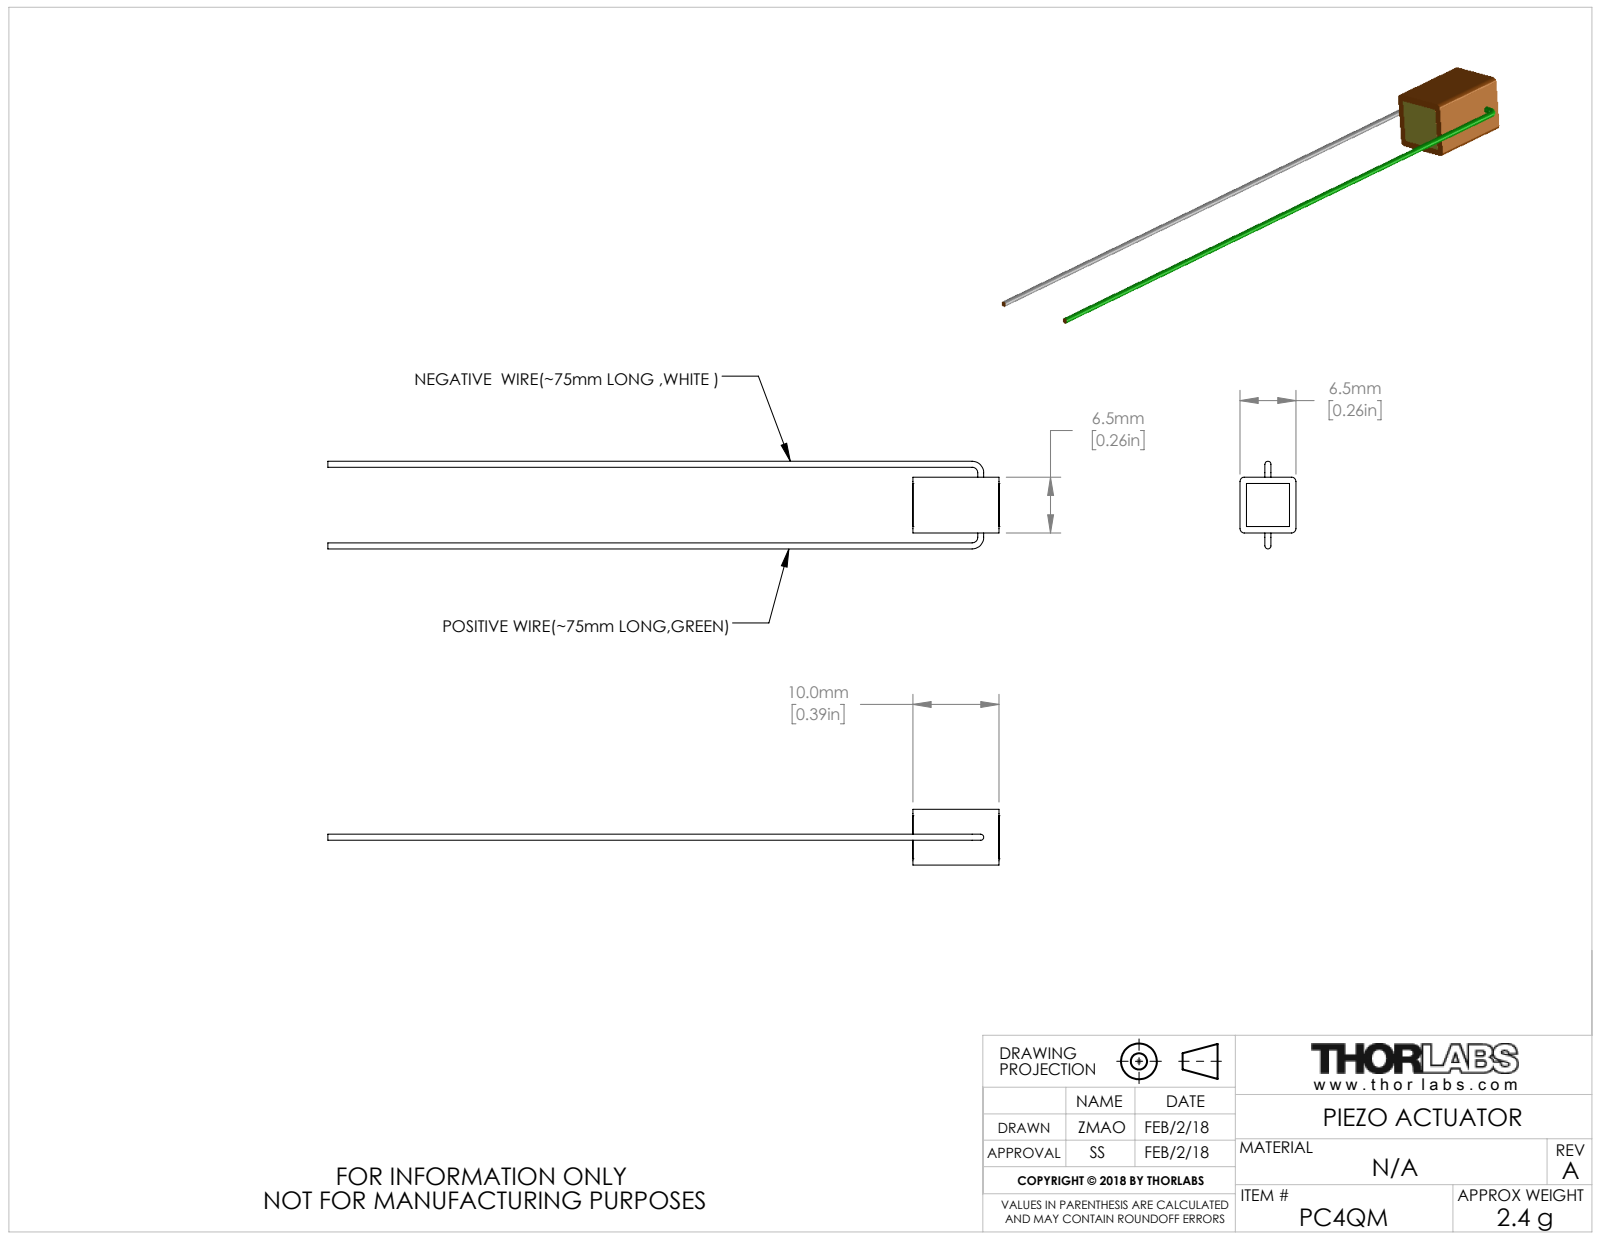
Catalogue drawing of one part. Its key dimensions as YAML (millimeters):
part_name: "CTN012214"
step_written_by: "SolidWorks 2016 (AUTOMOTIVE_DESIGN)"
units: millimeters
bodies: {solids: 1, faces: 34, planar: 18, cylindrical: 12, other: 4}
overall_size: [78.13, 10.2, 6.5]
volume: 480
surface_area: 675
round_bosses_or_shafts:
  - {diameter: 0.7, count: 3}
partial_cylinders:
  - {radius: 0.5, count: 4}
face_to_face_distances: [6.5, 10.01, 10.02, 10, 68.11, 68.12, 78.12, 78.13, 5.75, 0.75]
